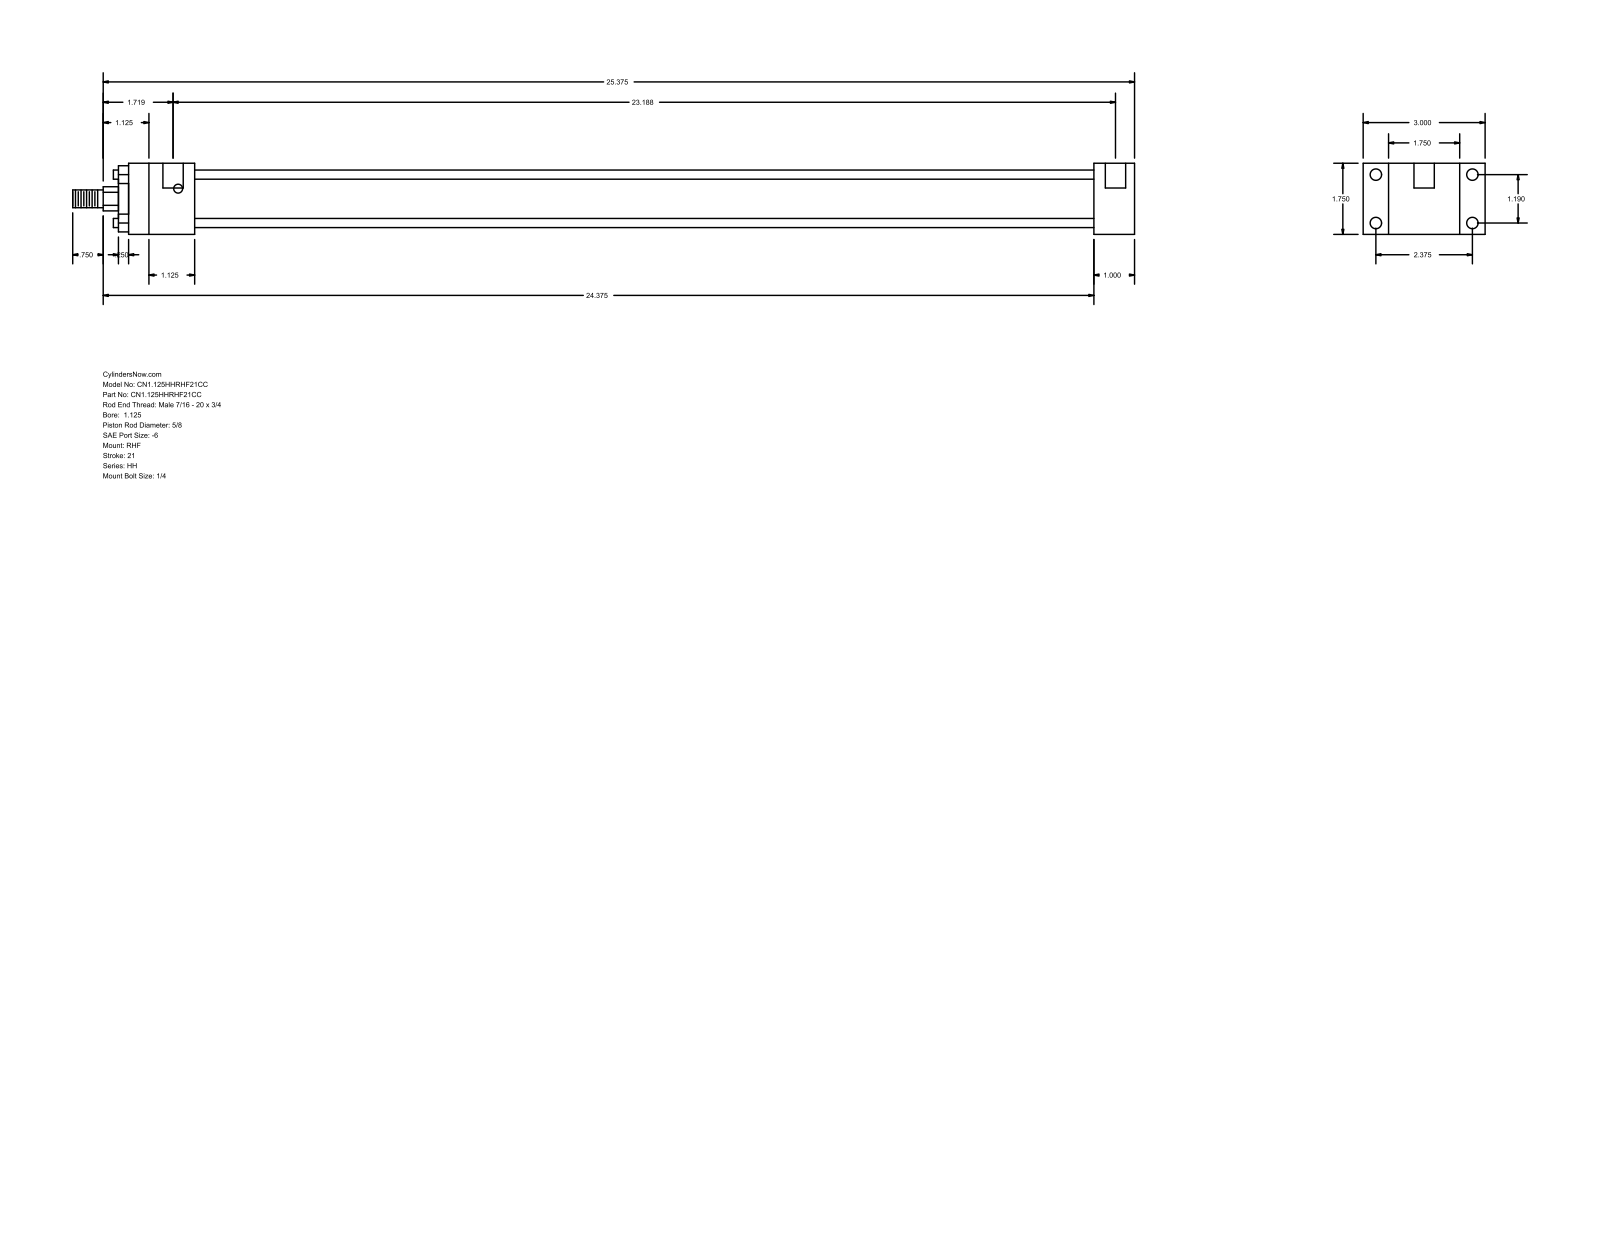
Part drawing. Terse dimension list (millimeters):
name: HH_RHF__0112_0.625
written by: GSSL Pune (CONFIG_CONTROL_DESIGN)
unit: mm
bodies: 0 solids, 88 faces (60 planar, 28 cylindrical, 0 other)
size: 663.58 × 76.2 × 44.45
holes: 4× ⌀5.56, 4× ⌀7.14, 2× ⌀12.7
bosses: 4× ⌀5.71, 1× ⌀34.92, 1× ⌀28.57, 1× ⌀15.88, 1× ⌀11.11
rounds: 1× R7.54
face distances: 44.46, 15.87, 25.4, 60.33, 76.2, 561.97, 587.37, 41.27, 603.24, 628.64
hole spacings: 30.22, 60.32, 67.47, 585.79, 3.17, 588.96
